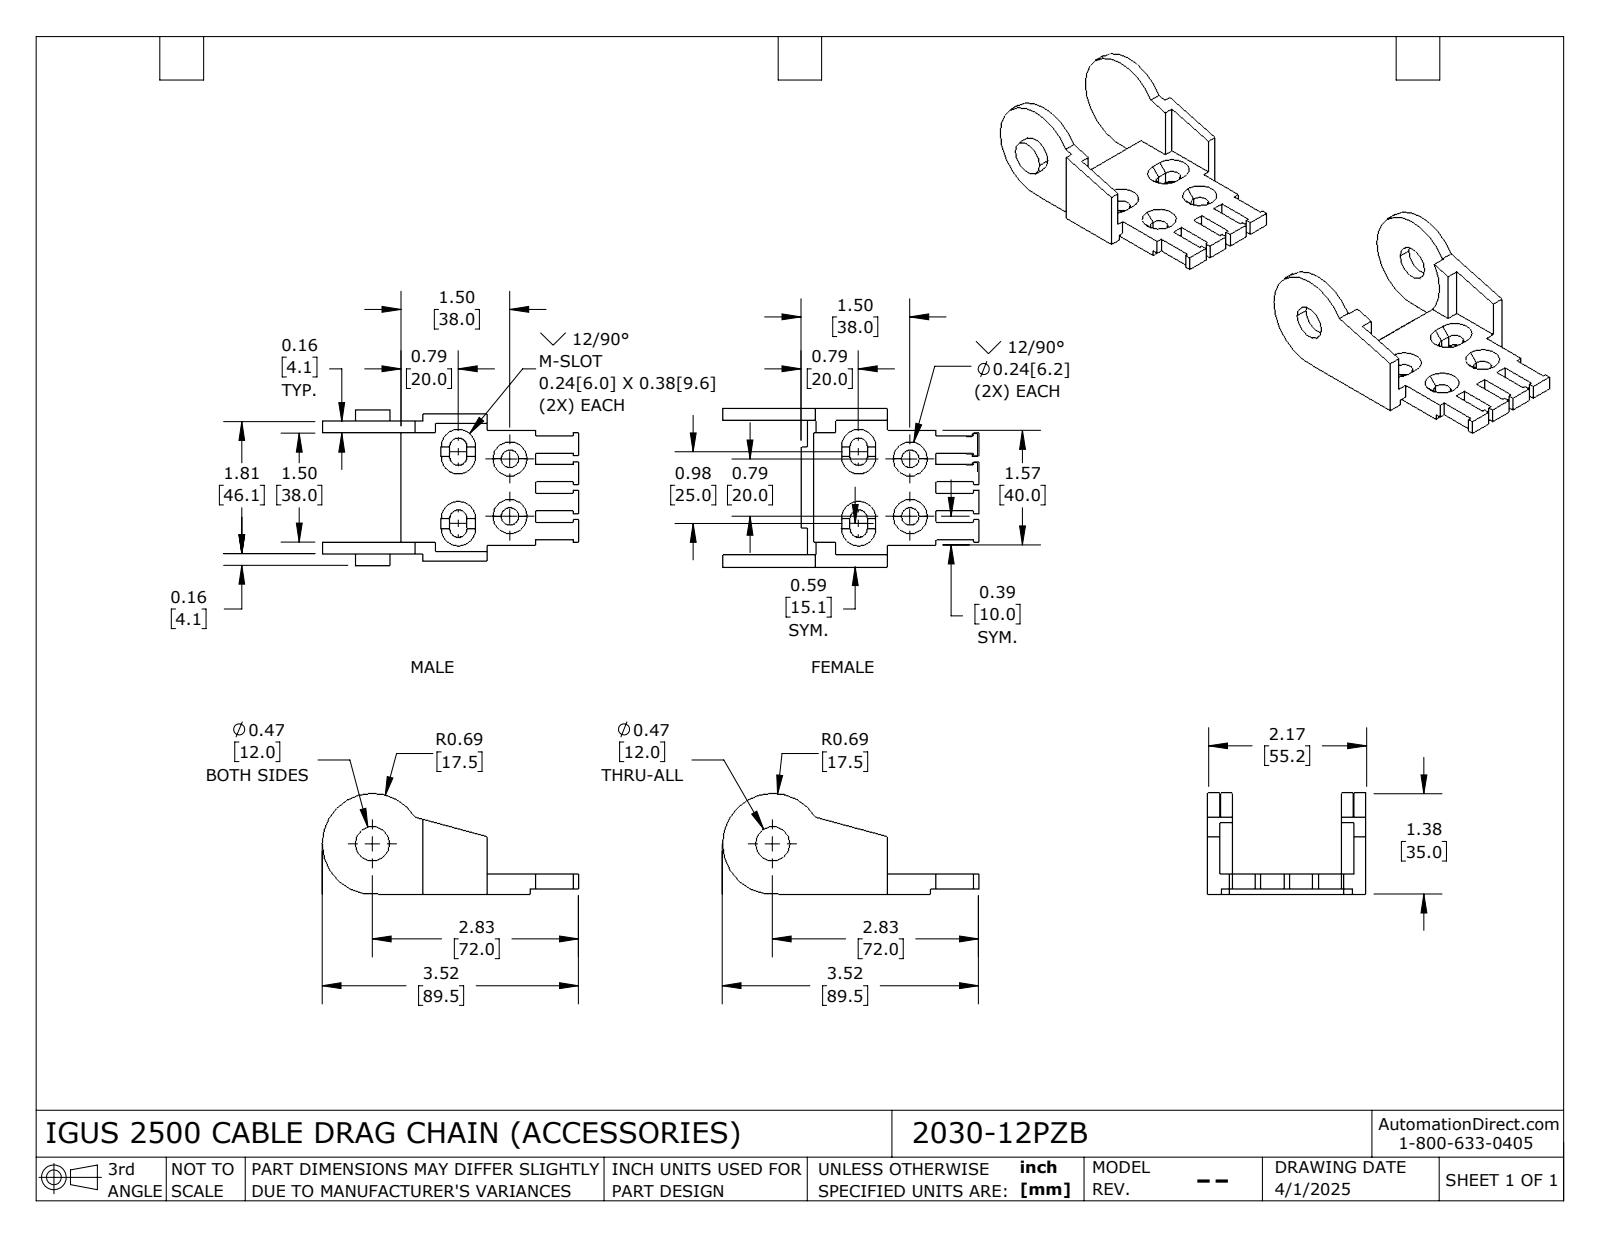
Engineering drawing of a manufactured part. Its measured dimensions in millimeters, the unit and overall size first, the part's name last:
Units: millimetres
Overall size (bounding box): 229.2 × 55.2 × 35
Round holes (diameter × count): ⌀6.2 ×4, ⌀12 ×1
Round bosses / shafts (diameter × count): ⌀12 ×1
Partial cylindrical surfaces — rounded edges, fillets, slot ends (radius × count): R3.05 ×8, R17.5 ×2, R17.7 ×1
Main face-to-face distances: 4.3, 7, 46.6, 42.3, 2, 8.6, 50.9, 4.55, 50.65, 46.35
Hole centre spacings: 20, 139.7, 141.12
Volume: 54 138 mm³ · Surface area: 28 611 mm²
Bodies: 2 solids, 203 faces (152 planar, 35 cylindrical, 16 other)
Part name (STEP PRODUCT): 2030-12PZB
STEP written by: SolidWorks 2024 (AUTOMOTIVE_DESIGN)
